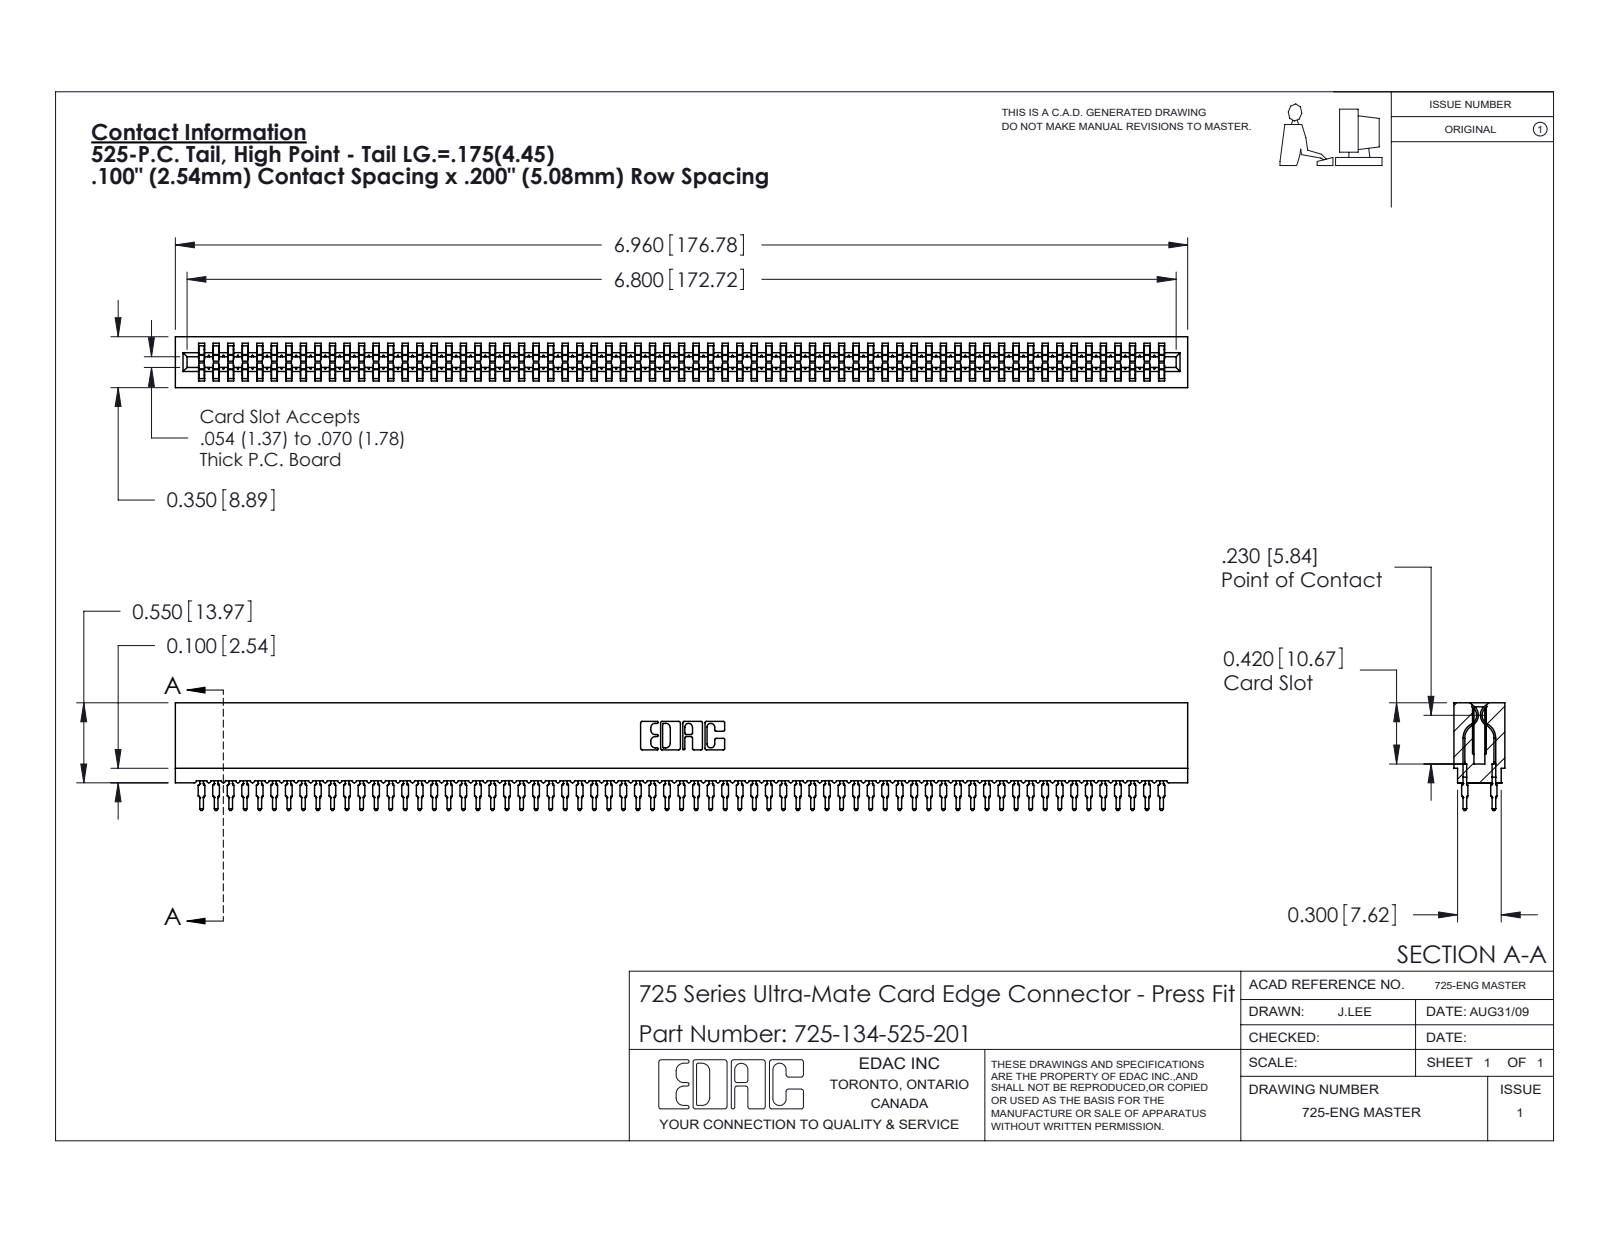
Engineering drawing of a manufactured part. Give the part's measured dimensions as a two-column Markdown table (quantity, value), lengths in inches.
| quantity | value |
| --- | --- |
| part name | 725-134-525-201; 745-292-001_525; 725 Part_Insulator Option - 01 |
| STEP written by | SolidWorks 2020 (CONFIG_CONTROL_DESIGN) |
| units | inches |
| bodies | 135 solids, 12088 faces (6219 planar, 2385 cylindrical, 3484 other) |
| overall size | 6.96 × 0.741 × 0.35 |
| volume | 0.846 in³ |
| surface area | 46.07 in² |
| partial cylindrical surfaces (radius × count) | 0.021 × 268, 0.015 × 134, 0.01 × 22, 0.005 × 8, 0.011 × 8, 0.007 × 6, 0.031 × 6, 0.026 × 3 |
| main face-to-face distances | 0.063, 0.287, 0.35, 0.212, 0.138, 0.076, 0.149, 0.045, 0.305, 0.018 |
